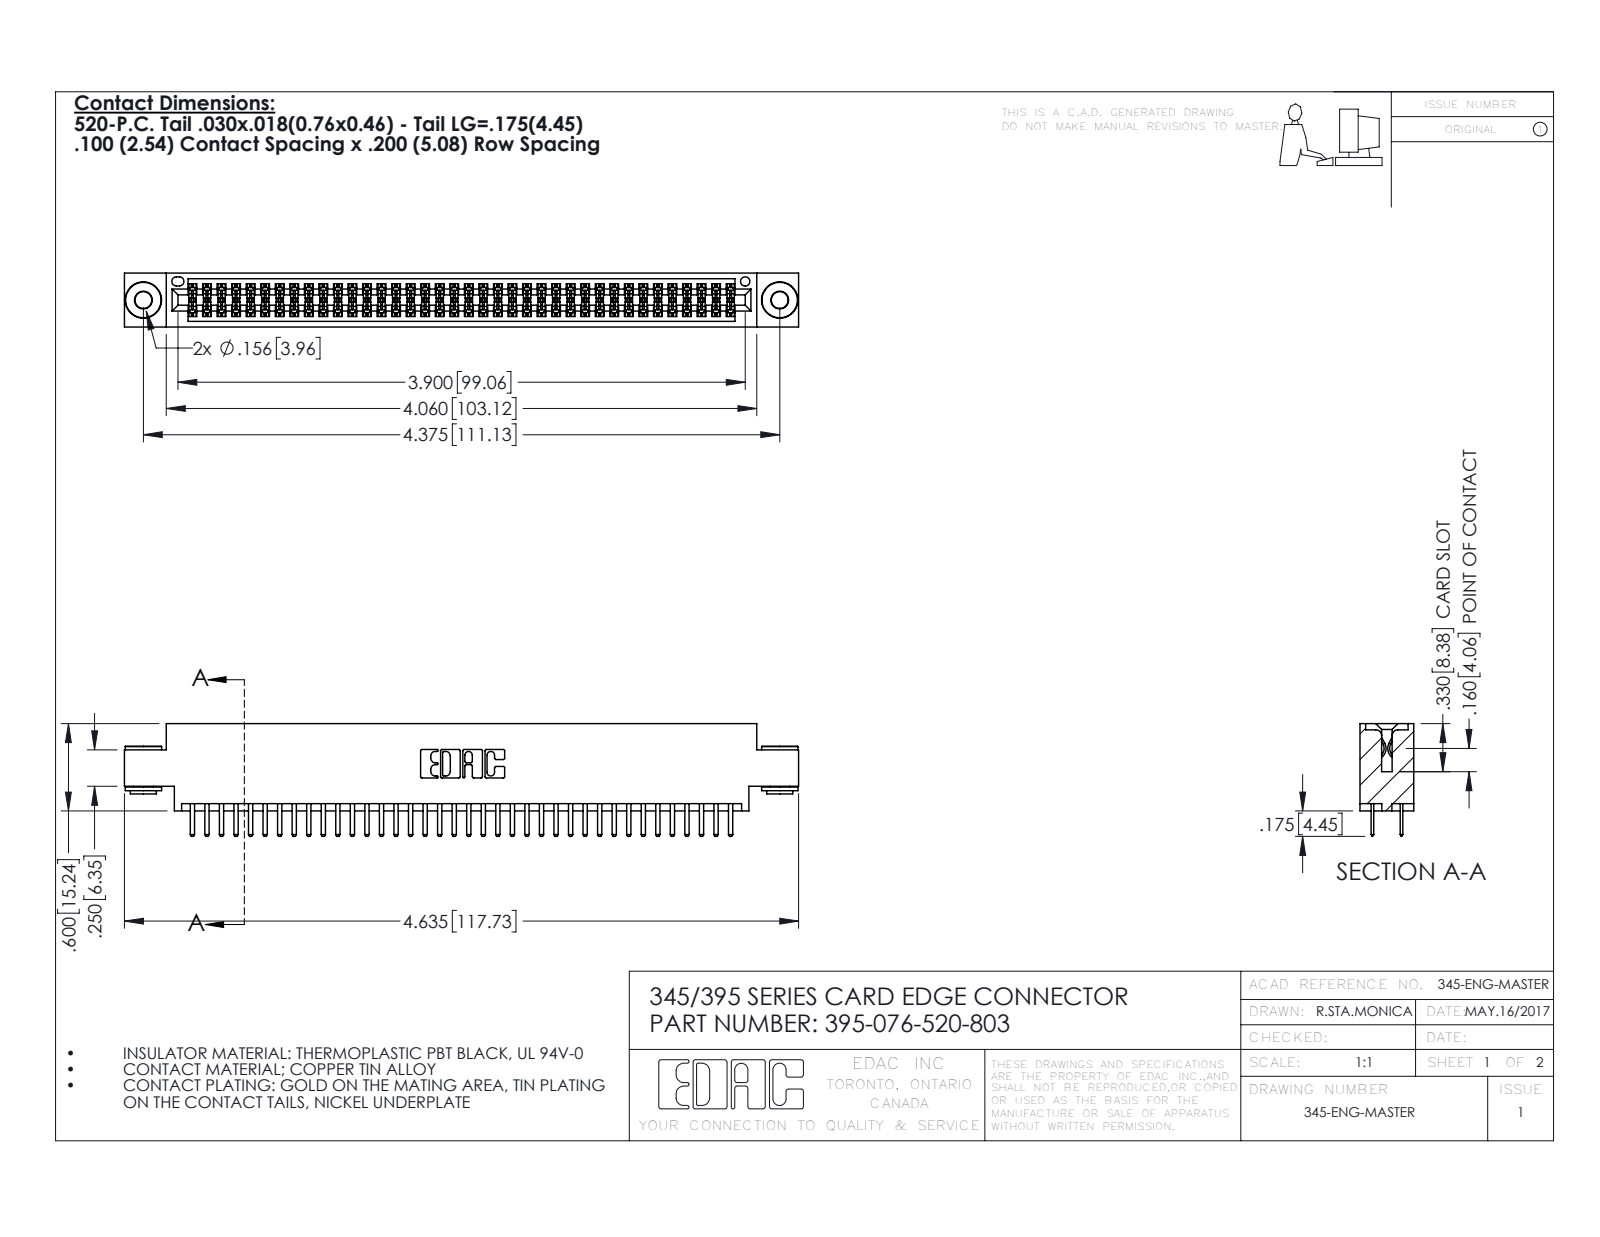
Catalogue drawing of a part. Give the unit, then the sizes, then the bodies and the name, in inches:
Units: inches
Overall size (bounding box): 4.635 × 0.775 × 0.37
Round holes (diameter × count): ⌀0.116 ×2, ⌀0.156 ×2, ⌀0.064 ×1
Round bosses / shafts (diameter × count): ⌀0.25 ×2, ⌀0.18 ×2, ⌀0.136 ×2
Partial cylindrical surfaces — rounded edges, fillets, slot ends (radius × count): R0.006 ×114, R0.01 ×80, R0.01 ×22, R0.007 ×6, R0.031 ×6, R0.026 ×3, R0.014 ×2, R0.019 ×2
Main face-to-face distances: 0.072, 0.298, 0.2, 0.37, 0.098, 0.272, 0.025, 0.225, 0.175, 0.022
Hole centre spacings: 0.27, 4.139, 4.375
Volume: 0.688 in³ · Surface area: 26.14 in²
Bodies: 79 solids, 4272 faces (2754 planar, 1510 cylindrical, 8 other)
Part name (STEP PRODUCT): 345 Part_0.170 Offset - 0.156 Dia-TH; 345-250-002_345-250-002-102; 345-292-001_345-293-120; 395-076-520-803
STEP written by: SolidWorks 2016 (CONFIG_CONTROL_DESIGN)
